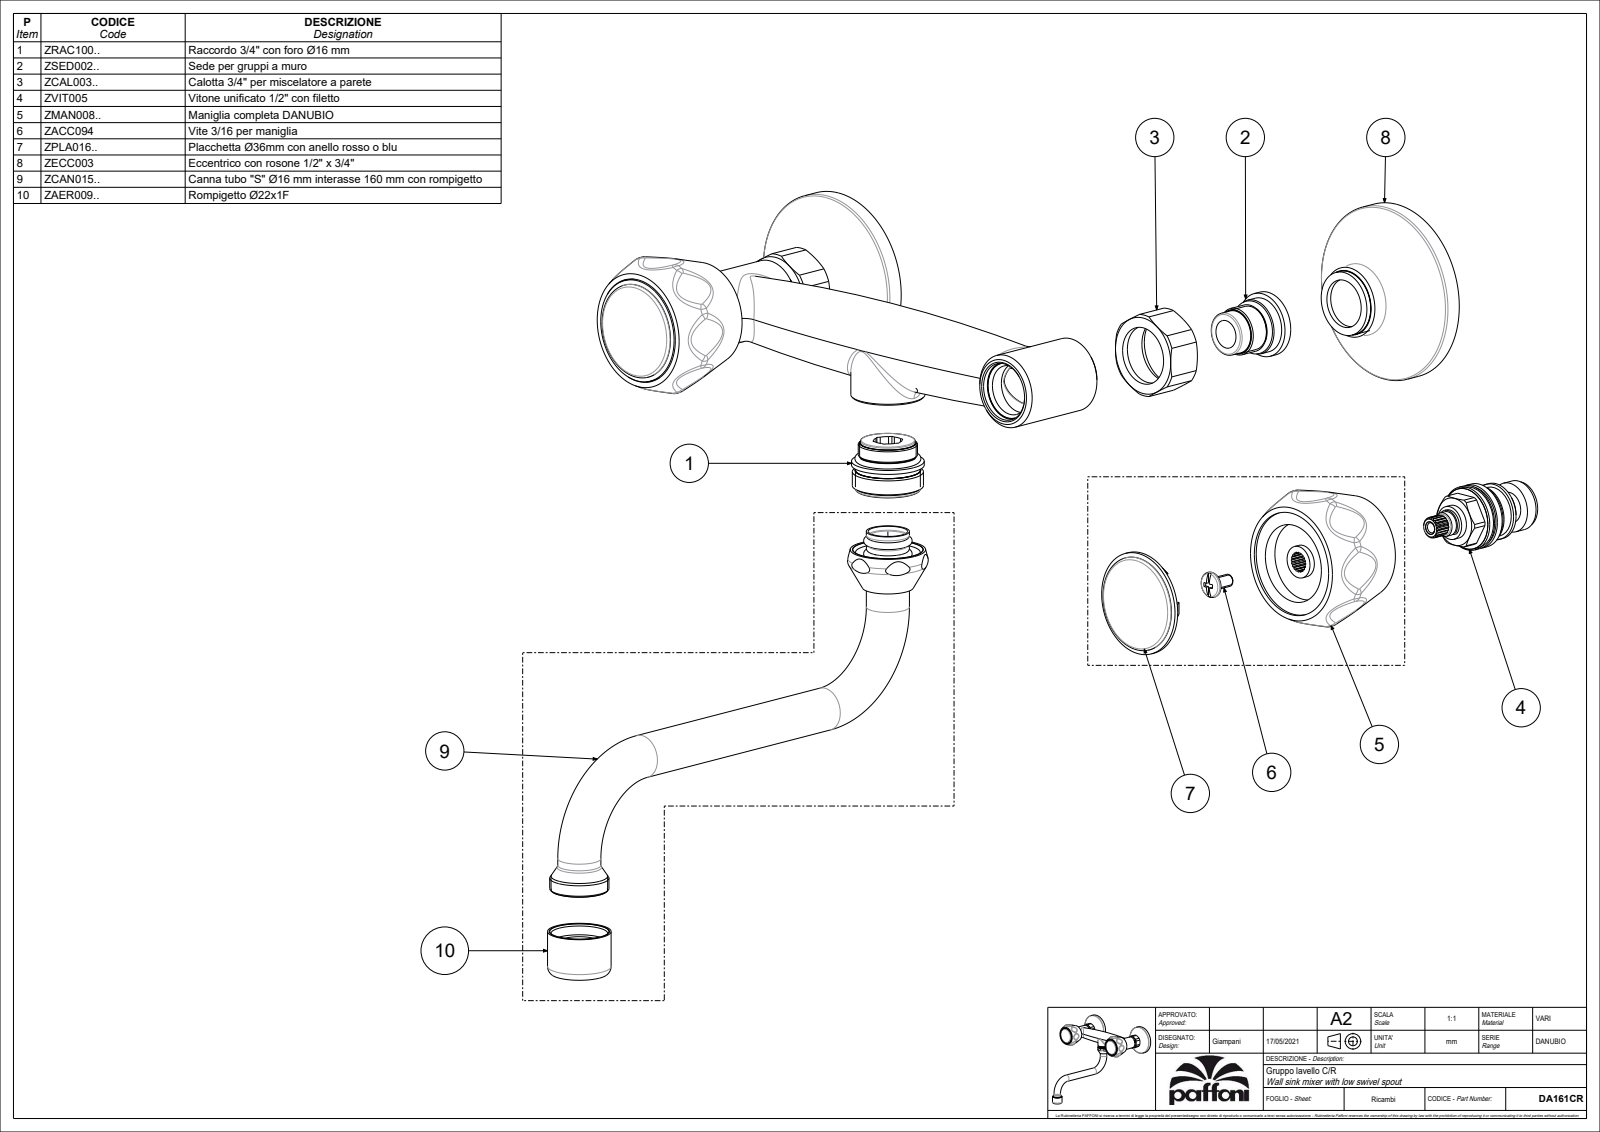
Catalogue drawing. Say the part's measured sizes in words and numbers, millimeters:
The part is named "DA161CR". Its 3-D file was written by "CREO PARAMETRIC BY PTC INC, 2020044 (CONFIG_CONTROL_DESIGN)". It is 3 solids with 497 faces: 79 planar, 142 cylindrical and 276 other. Overall it measures 226.8 by 224 by 168.9 millimeters. Its volume is 245 574 cubic millimeters and its surface area 104 107 square millimeters. Round holes: 3 of diameter 16.5, 3 of diameter 21.5, 3 of diameter 24, 2 of diameter 18.6, 2 of diameter 19, 2 of diameter 24.1, 2 of diameter 26.7, 2 of diameter 64, 1 of diameter 11.6, 1 of diameter 12.4, 1 of diameter 14.6, 1 of diameter 17.1. Round bosses or shafts: 3 of diameter 27.5, 3 of diameter 27, 3 of diameter 16, 2 of diameter 66, 2 of diameter 38.5, 1 of diameter 23.6, 1 of diameter 22, 1 of diameter 20.3. Partial cylindrical surfaces (rounded edges, fillets, slot ends): 16 of radius 21.31, 2 of radius 15.5, 1 of radius 5.25. The main face-to-face distances are 69.8, 69.67, 29, 35.3, 33, 79, 32.87, 36.8, 105.1, 104.97. The hole center spacings are 158.
